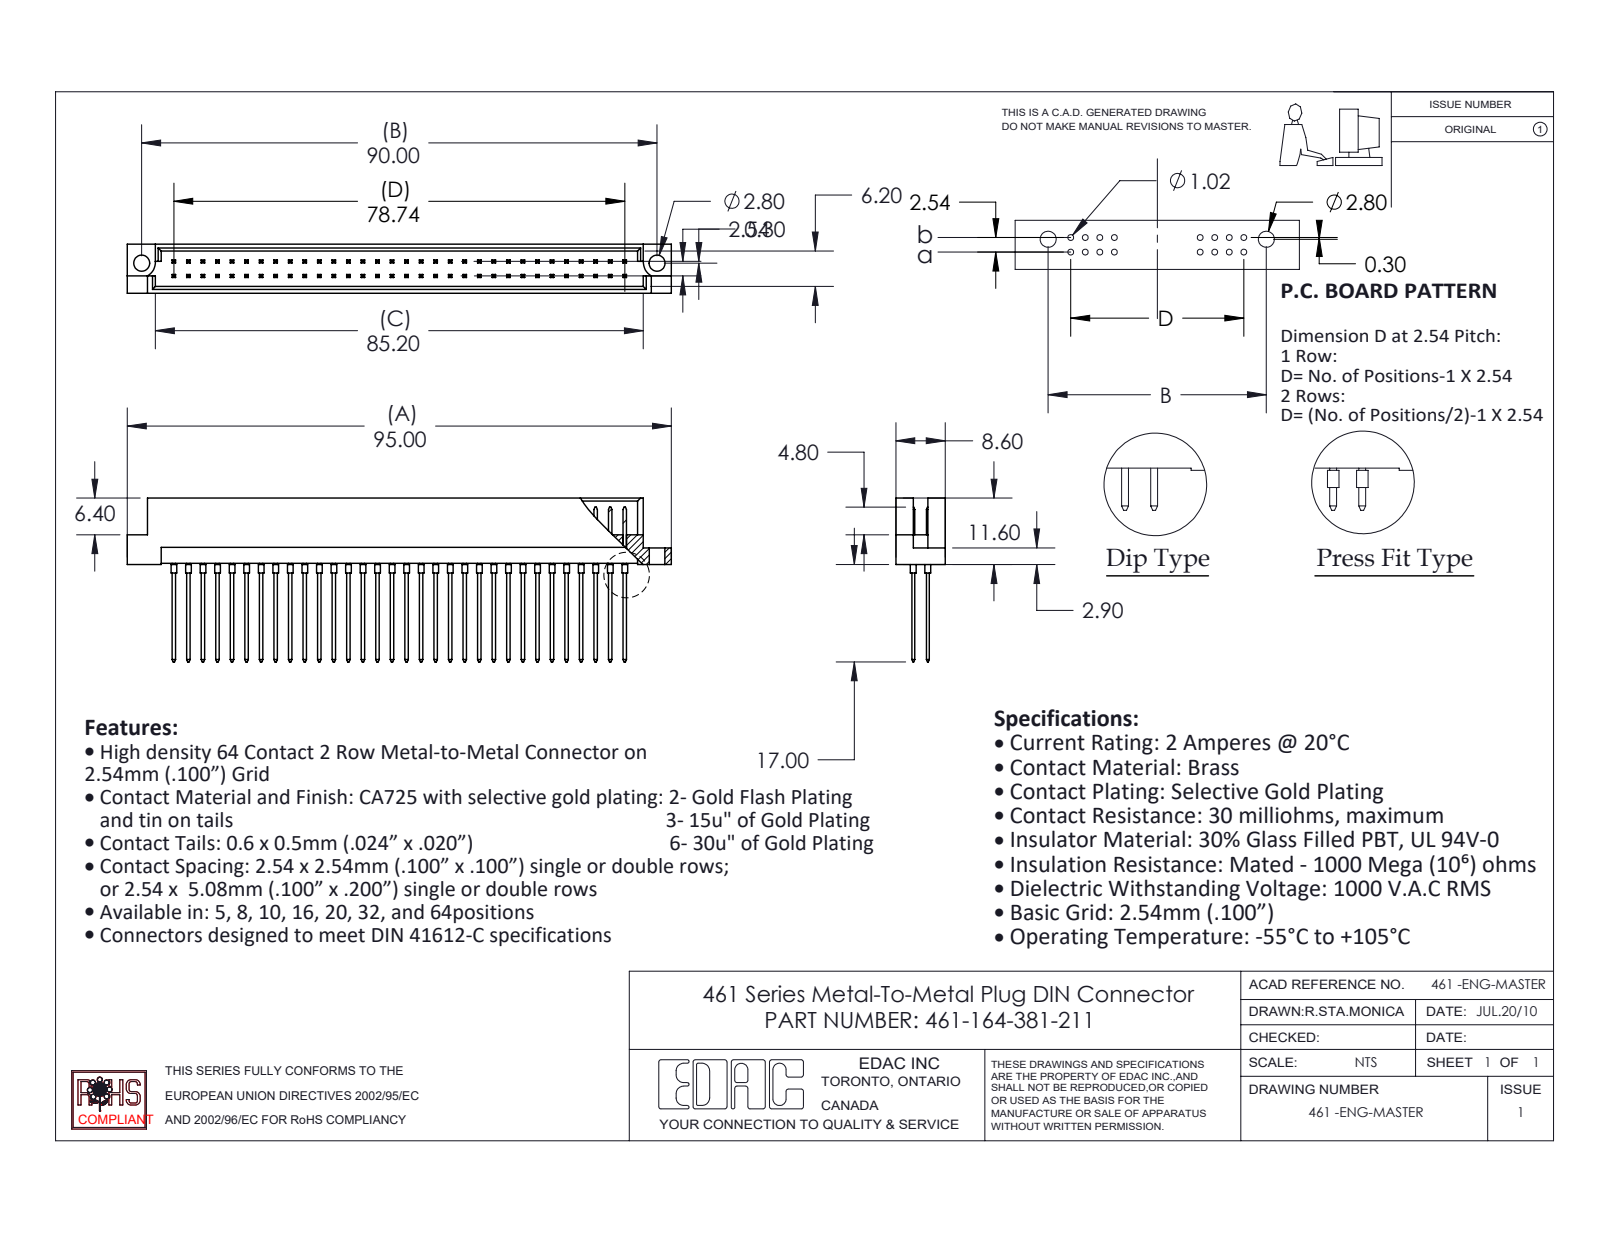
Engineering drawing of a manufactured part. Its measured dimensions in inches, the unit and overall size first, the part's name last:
Units: inches
Overall size (bounding box): 3.74 × 1.126 × 0.339
Round holes (diameter × count): ⌀0.11 ×2
Round bosses / shafts (diameter × count): ⌀0.039 ×64
Partial cylindrical surfaces — rounded edges, fillets, slot ends (radius × count): R0.11 ×2
Main face-to-face distances: 0.1, 0.047, 0.291, 0.129, 0.209, 0.082, 0.162, 0.109, 0.229, 0.062
Hole centre spacings: 3.543
Volume: 0.318 in³ · Surface area: 14.88 in²
Bodies: 65 solids, 1713 faces (1578 planar, 135 cylindrical, 0 other)
Part name (STEP PRODUCT): 461-290_81; 461 Part_64; 461-164-381-211
STEP written by: SolidWorks 2020 (CONFIG_CONTROL_DESIGN)
